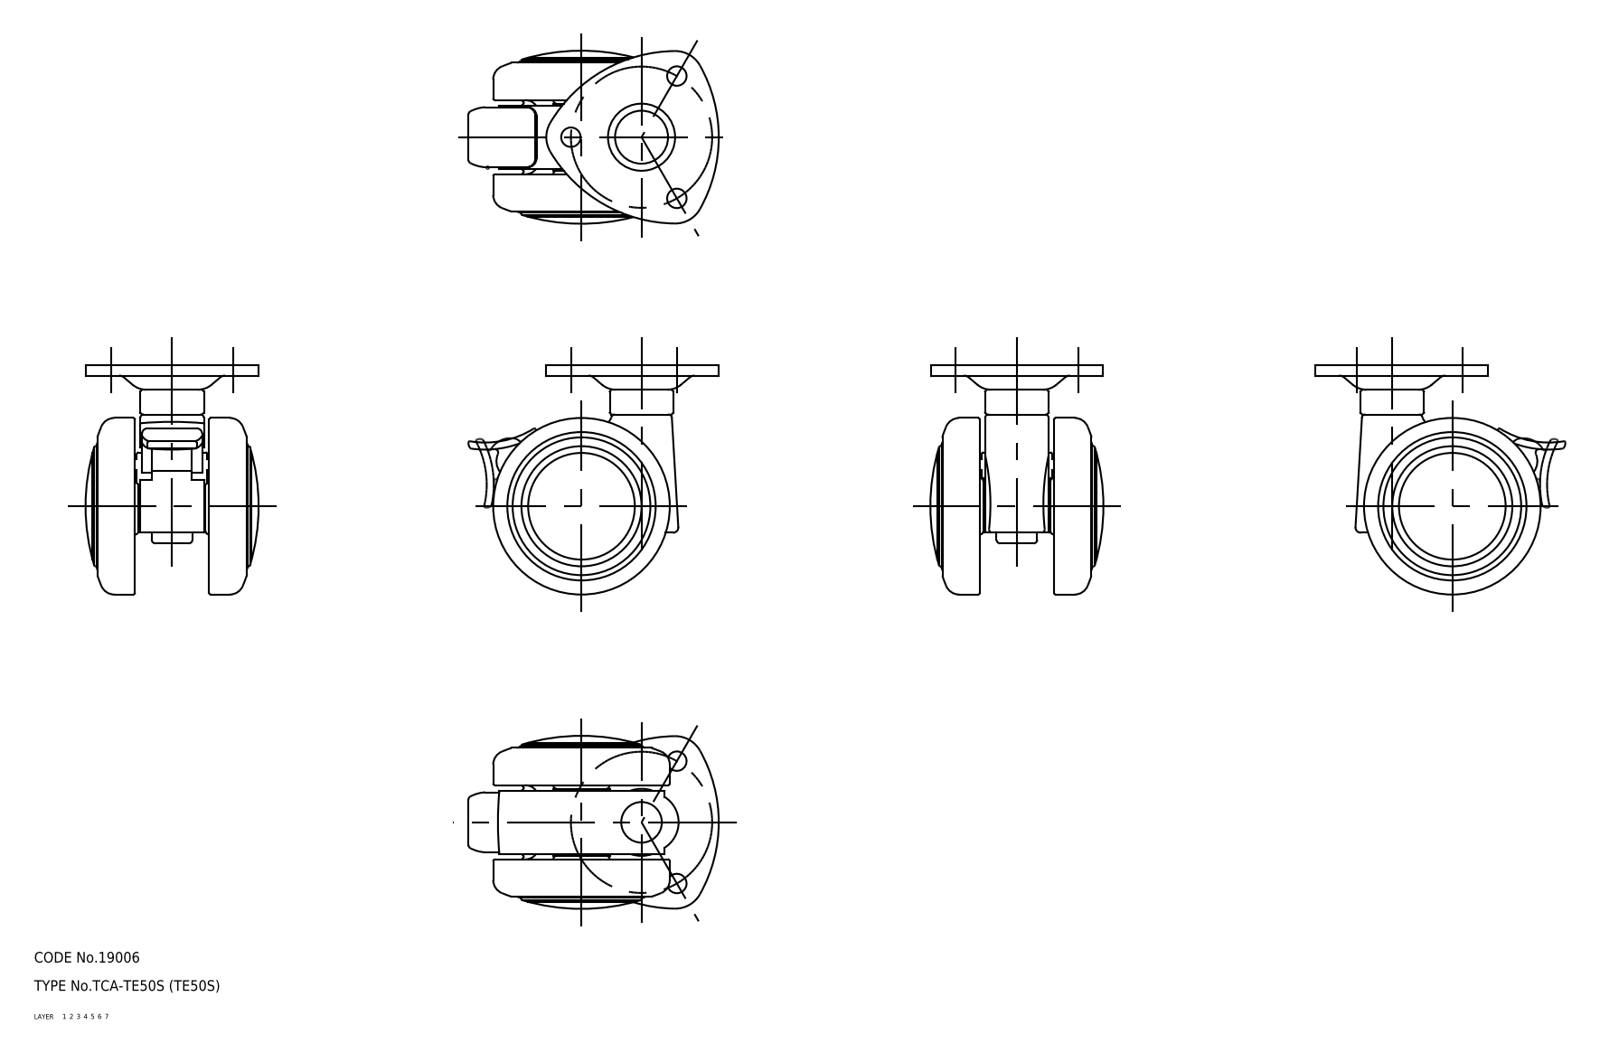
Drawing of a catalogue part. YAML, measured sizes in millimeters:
part_name: "wheel; mounting plate; main shaft; lever (+1 more)"
step_written_by: "CADfix (AUTOMOTIVE_DESIGN)"
units: millimeters
bodies: {solids: 6, faces: 244, planar: 0, cylindrical: 0, other: 244}
overall_size: [70.82, 65, 49]
volume: 68151
surface_area: 31772
